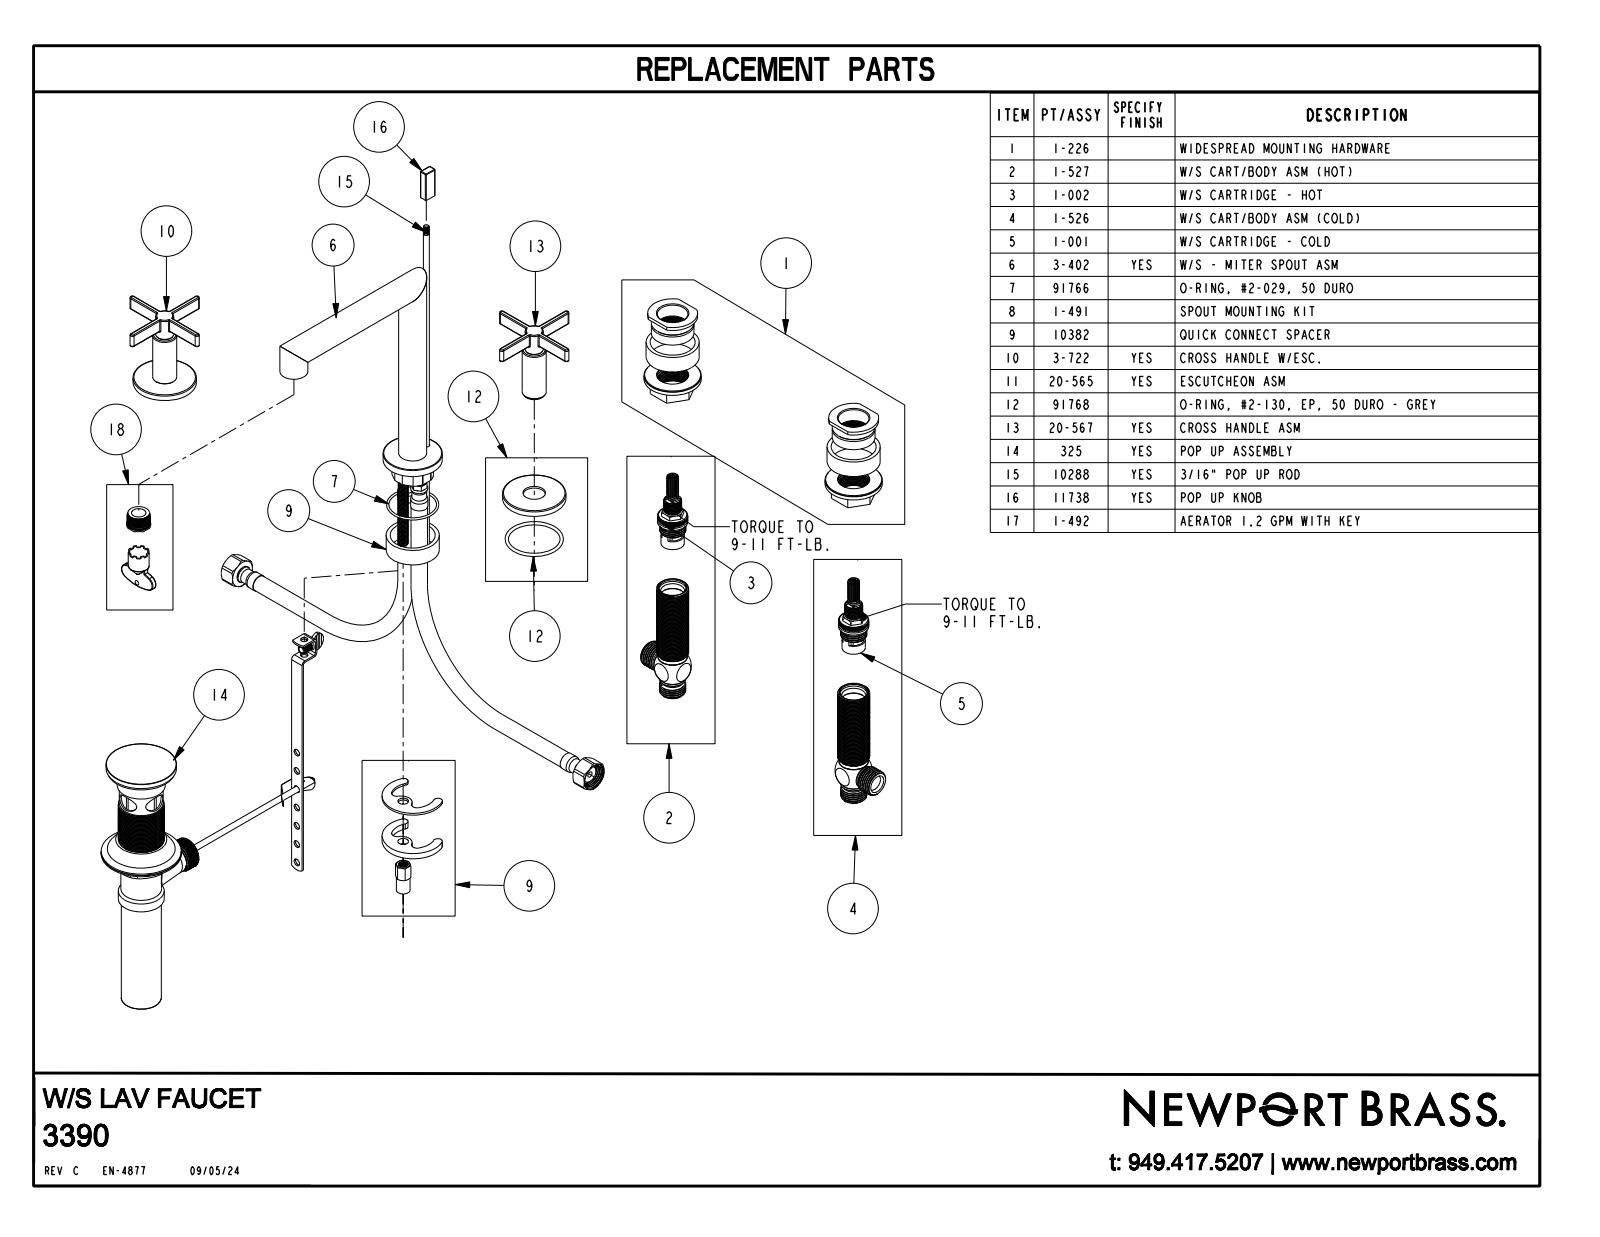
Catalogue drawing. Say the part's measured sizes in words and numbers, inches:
The part is named "3390". Its 3-D file was written by "CREO PARAMETRIC BY PTC INC, 2019352 (CONFIG_CONTROL_DESIGN)". It is 4 solids with 223 faces: 47 planar, 94 cylindrical and 82 other. Overall it measures 11 by 7.188 by 7.089 inches. Its volume is 11.78 cubic inches and its surface area 79.92 square inches. Round holes: 1 of diameter 0.721. Round bosses or shafts: 3 of diameter 0.875, 2 of diameter 1.98, 2 of diameter 0.75, 2 of diameter 0.73, 2 of diameter 0.563, 2 of diameter 0.51, 1 of diameter 1.85. Partial cylindrical surfaces (rounded edges, fillets, slot ends): 28 of radius 0.03, 8 of radius 0.075, 6 of radius 0.02, 1 of radius 0.47, 1 of radius 0.876. The main face-to-face distances are 0.2, 0.25, 0.05, 0.15, 0.15, 8, 2.551, 2.351, 2.301, 8.15.
